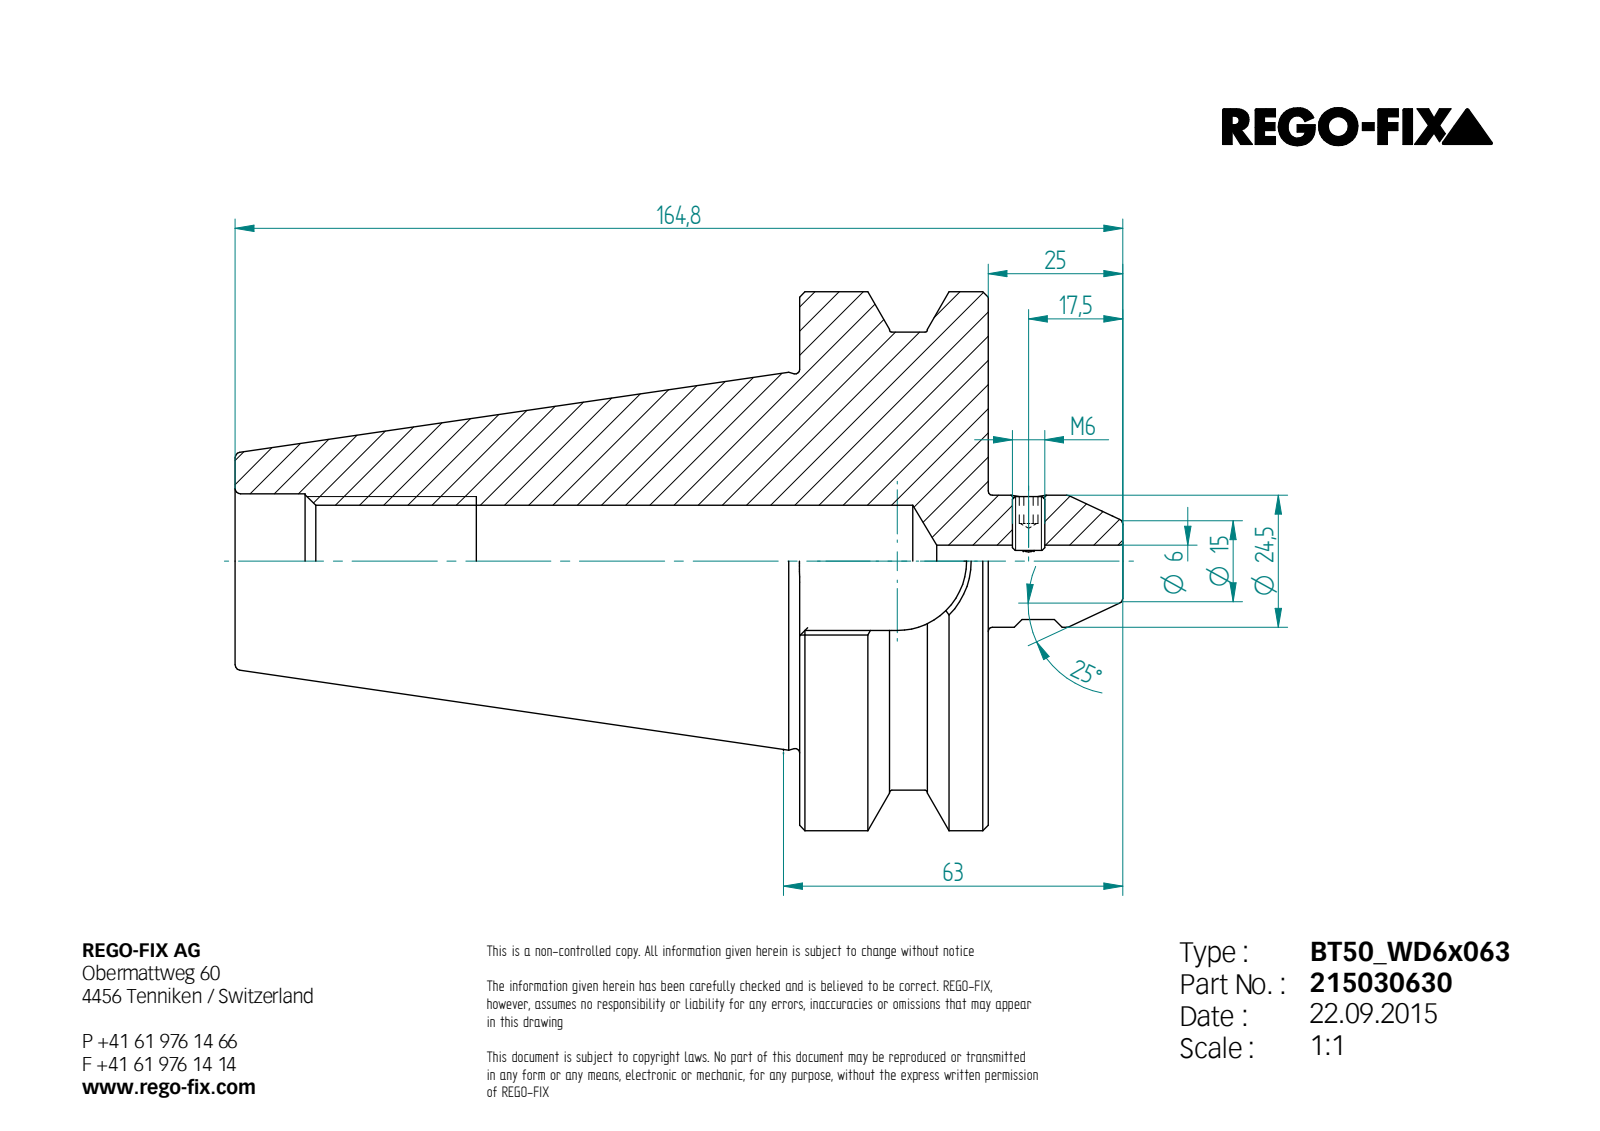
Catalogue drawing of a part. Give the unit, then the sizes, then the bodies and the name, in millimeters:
Units: millimetres
Overall size (bounding box): 164.8 × 100 × 100
Round holes (diameter × count): ⌀4.92 ×1, ⌀6 ×1, ⌀20.75 ×1, ⌀25 ×1
Round bosses / shafts (diameter × count): ⌀100 ×1, ⌀85 ×1, ⌀24.5 ×1, ⌀6 ×1
Partial cylindrical surfaces — rounded edges, fillets, slot ends (radius × count): R0.5 ×4, R12.85 ×1
Main face-to-face distances: 35, 70.7, 104.8, 139.8, 25.7, 164.8, 60, 25, 2.05, 23.65
Volume: 457 398 mm³ · Surface area: 55 453 mm²
Bodies: 2 solids, 94 faces (45 planar, 18 cylindrical, 31 other)
STEP written by: Unknown (AUTOMOTIVE_DESIGN)
